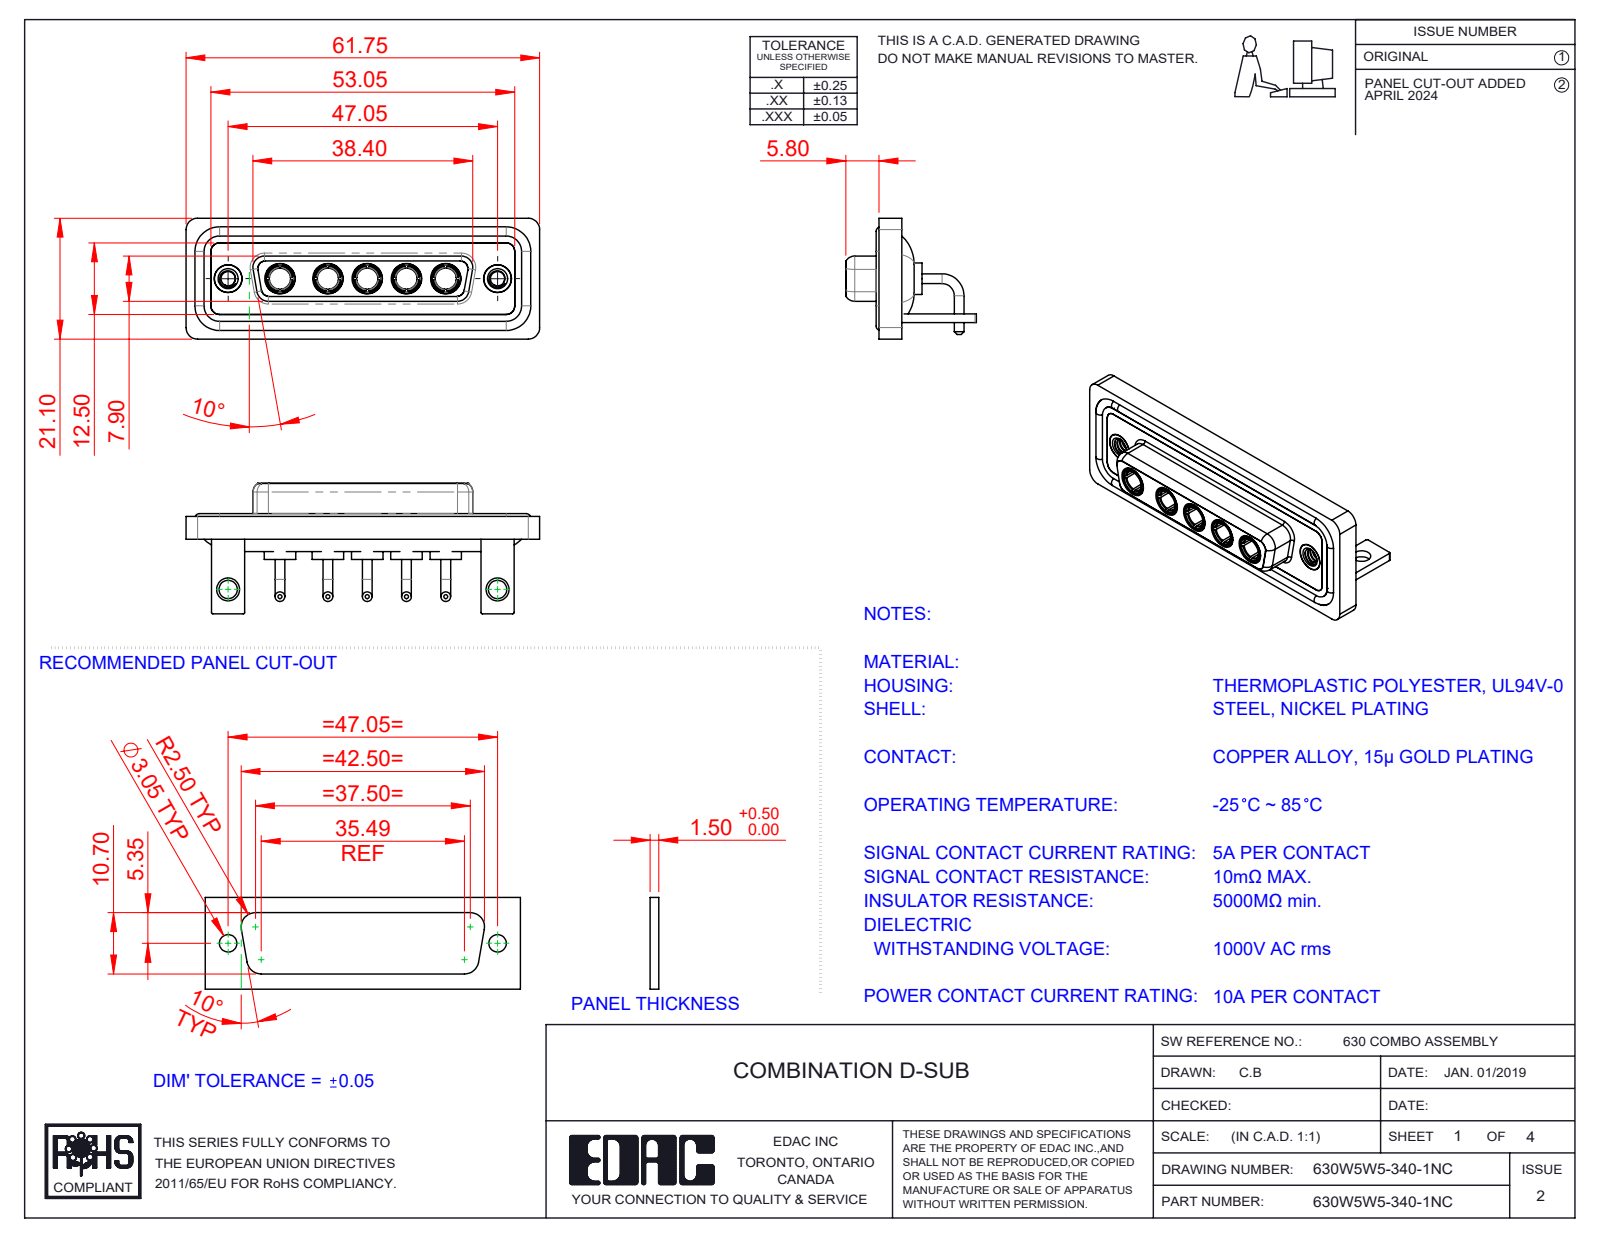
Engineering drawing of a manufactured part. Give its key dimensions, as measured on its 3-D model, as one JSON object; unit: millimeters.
{"part_name": "Power Socket_10A RA; 630Combo Shell Rear_25 Contacts; 630Combo Threaded Rivet_A; 630Combo Stabilizer Bracket_50 Contacts (+4 more)", "step_written_by": "SolidWorks 2023 (CONFIG_CONTROL_DESIGN)", "units": "millimeters", "bodies": {"solids": 19, "faces": 818, "planar": 270, "cylindrical": 335, "other": 213}, "overall_size": [61.75, 22.8, 21.1], "volume_mm3": 8506, "surface_area_mm2": 14298, "round_holes": [[4.85, 7], [3.7, 5], [5.3, 5], [2.5, 2], [3.2, 2], [4, 2], [4.05, 2], [5, 2]], "round_bosses_or_shafts": [[1.7, 10], [5.5, 5], [5.2, 5], [4.96, 5], [4.75, 5], [3.75, 5], [1.6, 4], [4.95, 2]], "partial_cylinders_radius": [[2, 19], [1.5, 18], [0.25, 16], [1.35, 8], [1.6, 8], [0.5, 5], [2.1, 5], [0.6, 4]], "face_to_face_distances": [0.4, 1.8, 1.5, 2.9, 3.7, 4.1, 1.1, 1.4, 1.6, 2.5], "hole_center_spacings": [6.86, 9.04, 38.01, 47.05, 6.87, 8.38, 13.72, 13.73]}
